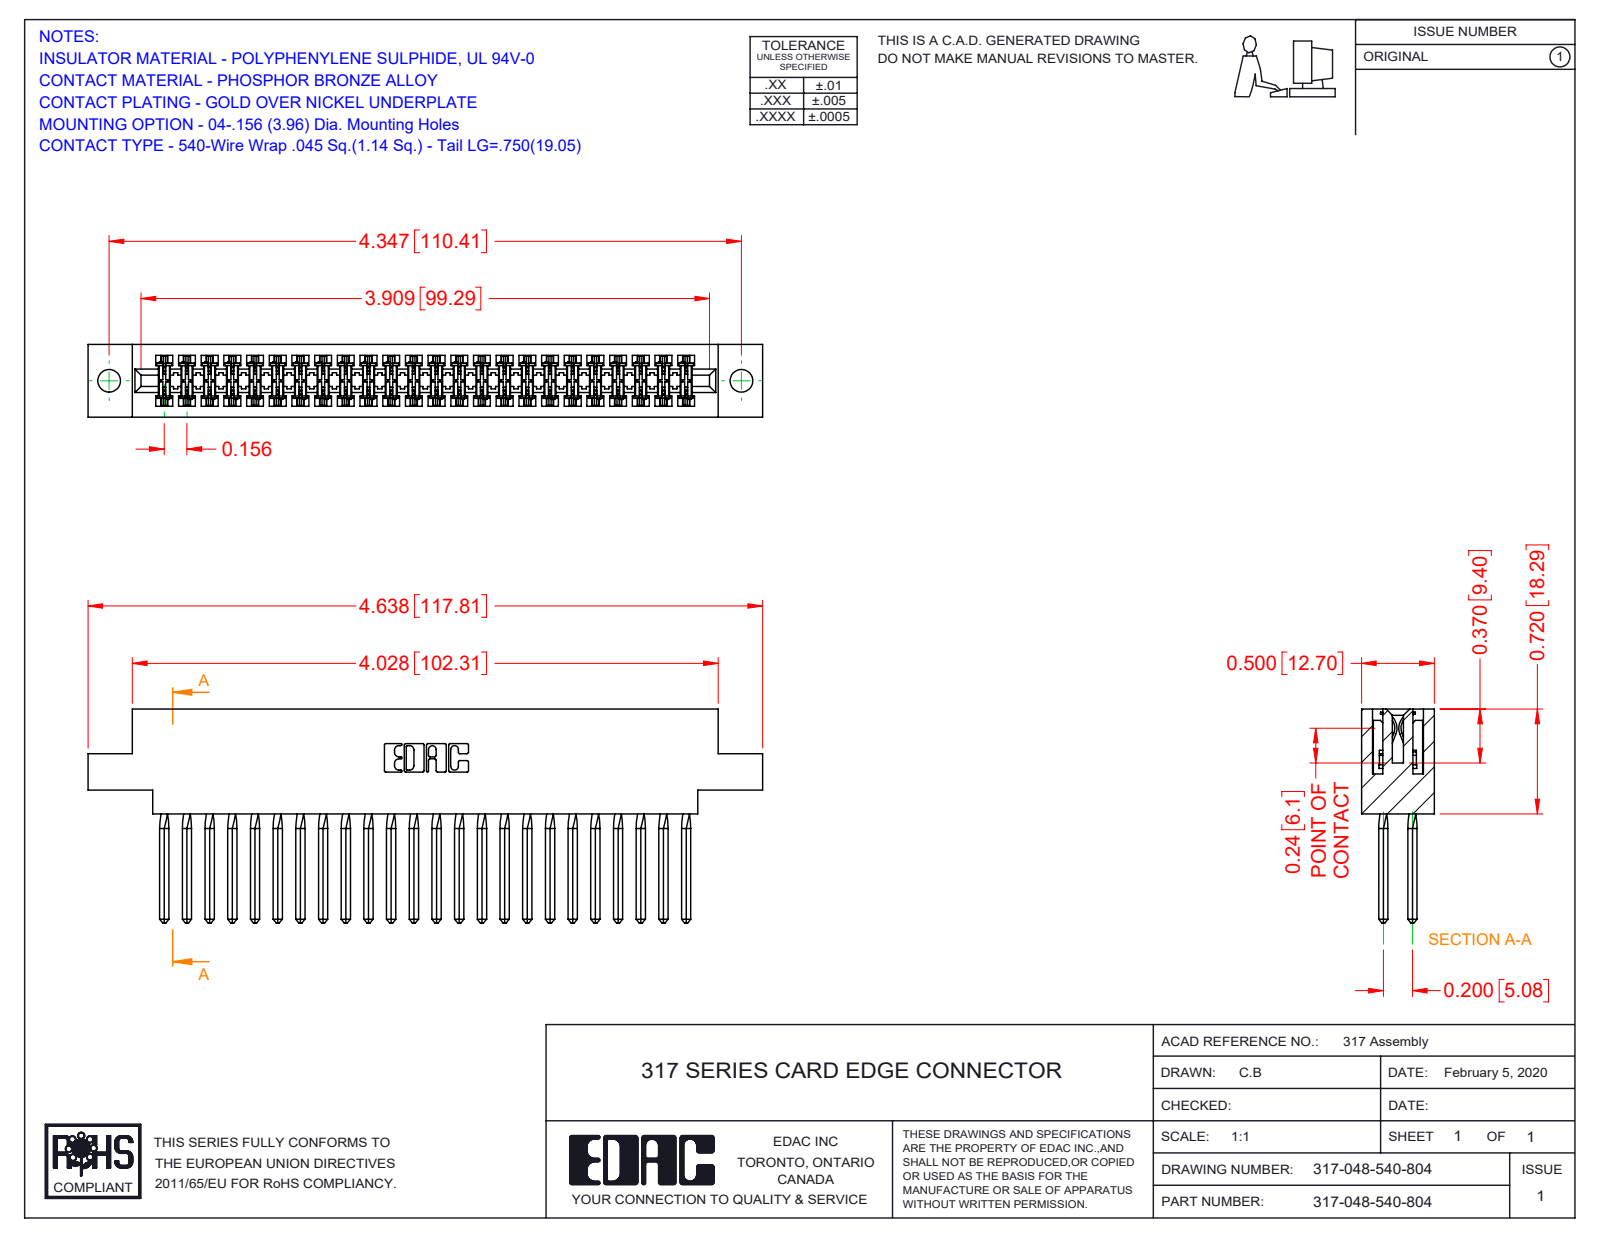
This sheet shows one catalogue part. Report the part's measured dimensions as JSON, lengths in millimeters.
{"part_name": "317 Part_.156 Dia - TH; 317-290-001_540; 317-048-540-804", "step_written_by": "SolidWorks 2016 (CONFIG_CONTROL_DESIGN)", "units": "millimeters", "bodies": {"solids": 49, "faces": 4374, "planar": 3562, "cylindrical": 620, "other": 192}, "overall_size": [117.8, 37.3, 12.7], "volume_mm3": 19070, "surface_area_mm2": 27590, "round_holes": [[4, 2]], "partial_cylinders_radius": [[0.4, 96], [0.3, 22], [0.2, 6], [0.8, 6], [0.7, 3], [2.4, 2], [2.5, 2], [2.8, 2]], "face_to_face_distances": [12.7, 1.9, 10.8, 8.9, 2.8, 5, 2.4, 18.3, 5.1, 2.9], "hole_center_spacings": [110.4]}
